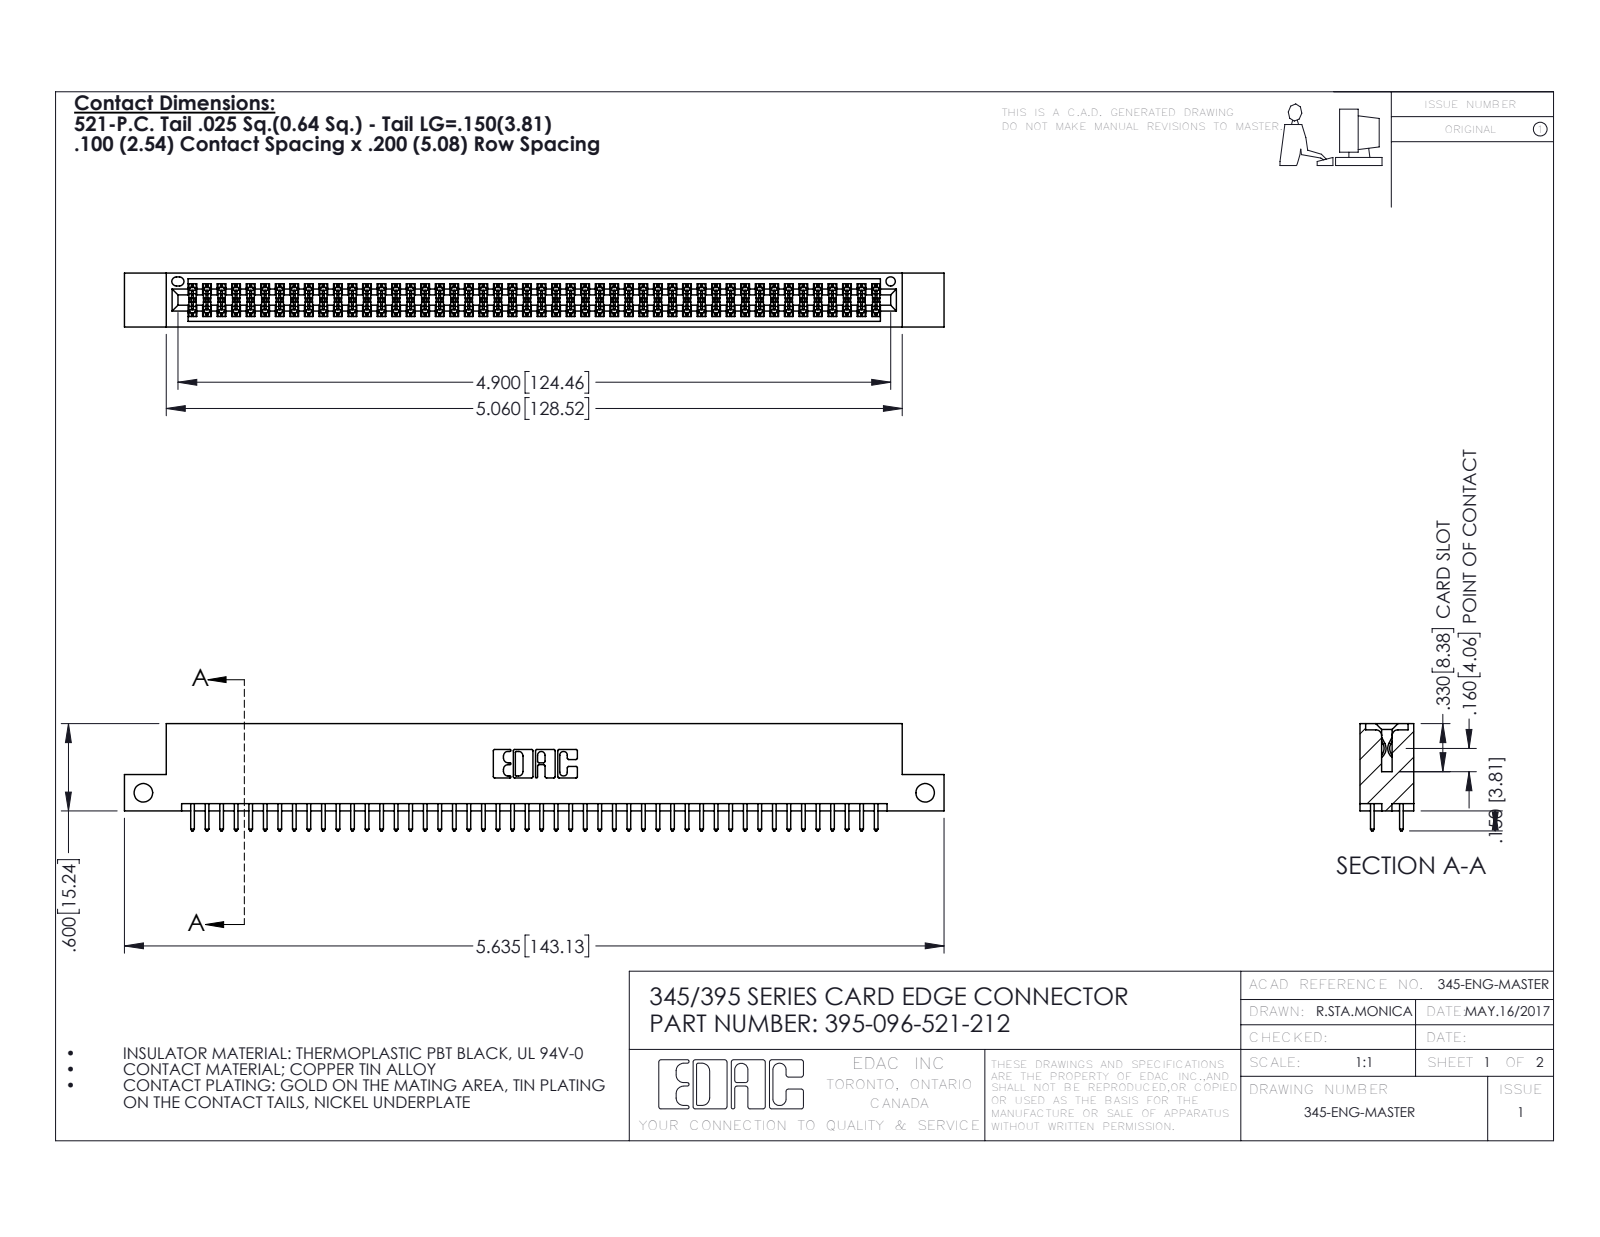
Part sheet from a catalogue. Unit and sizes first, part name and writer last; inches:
Units: inches
Overall size (bounding box): 5.635 × 0.737 × 0.37
Round holes (diameter × count): ⌀0.128 ×2, ⌀0.064 ×1
Partial cylindrical surfaces — rounded edges, fillets, slot ends (radius × count): R0.006 ×144, R0.01 ×96, R0.01 ×22, R0.007 ×6, R0.031 ×6, R0.026 ×3, R0.014 ×2, R0.019 ×2
Main face-to-face distances: 0.298, 0.072, 0.2, 0.37, 0.098, 0.272, 0.025, 0.225, 0.175, 0.149
Hole centre spacings: 5.375
Volume: 0.844 in³ · Surface area: 31.27 in²
Bodies: 97 solids, 4926 faces (3248 planar, 1678 cylindrical, 0 other)
Part name (STEP PRODUCT): 345-292-001_345-293-121; 345 Part_Flush Mounting Lugs - Side Mount; 395-096-521-212
STEP written by: SolidWorks 2016 (CONFIG_CONTROL_DESIGN)
